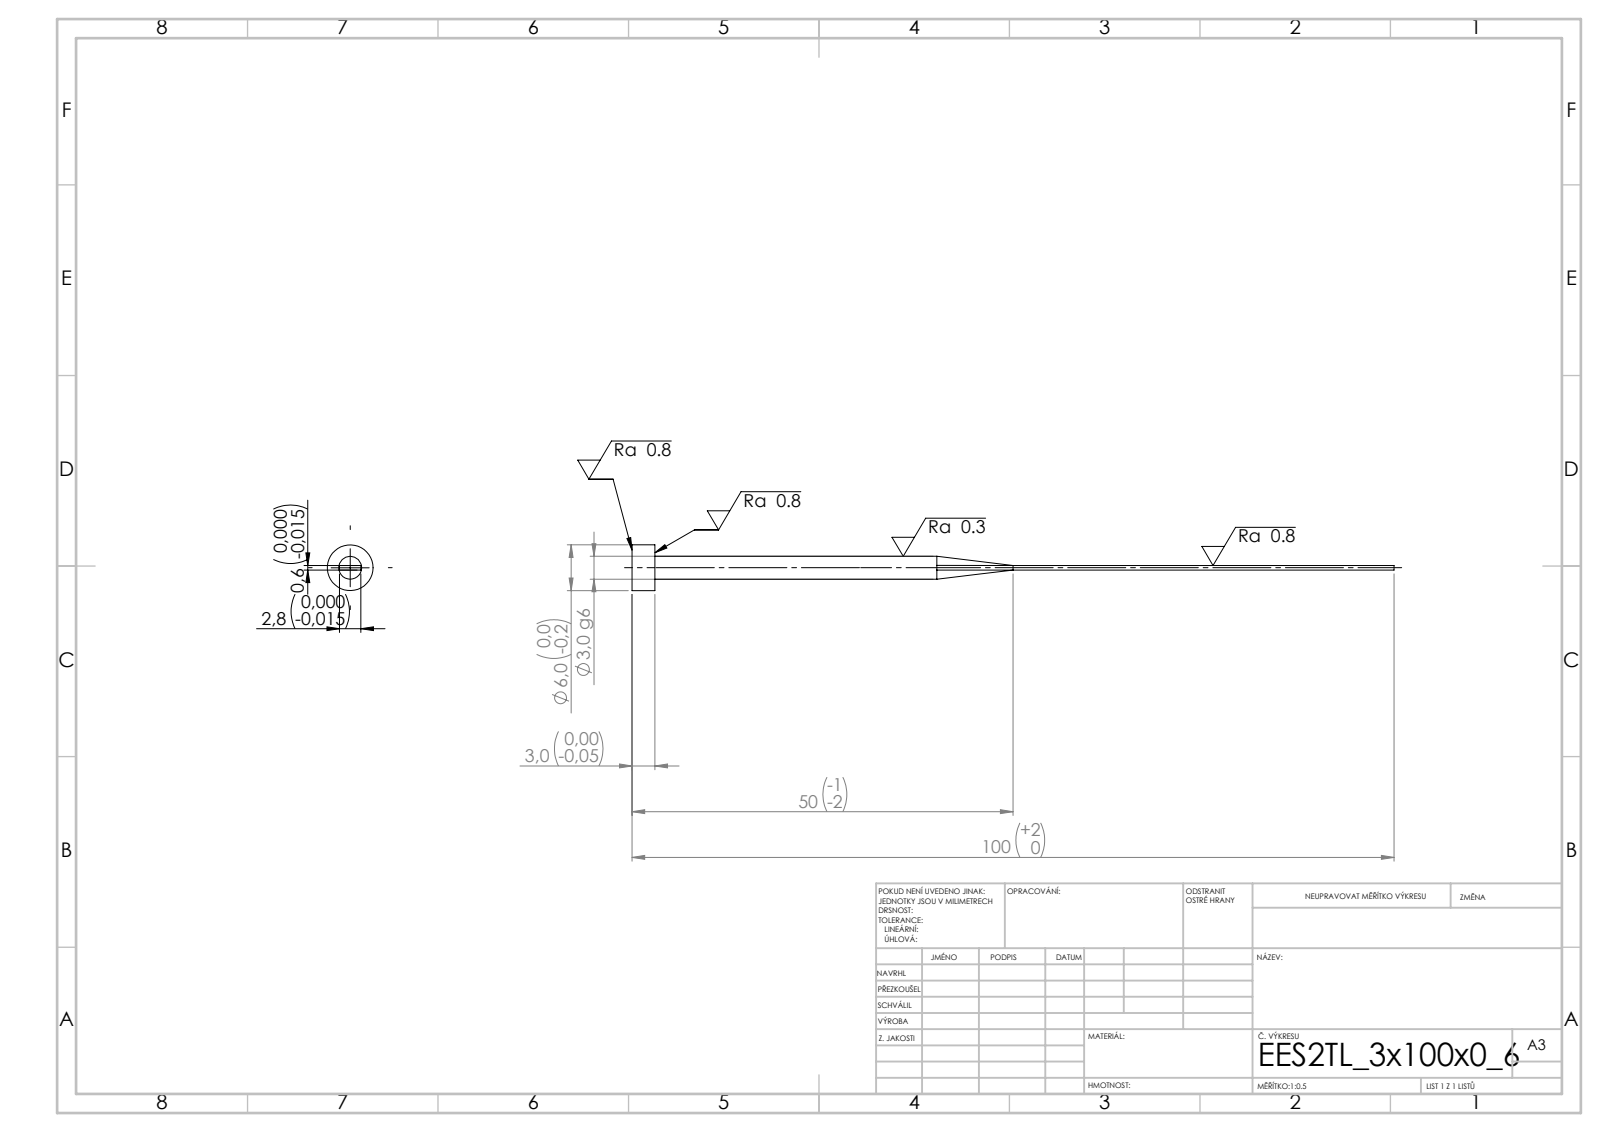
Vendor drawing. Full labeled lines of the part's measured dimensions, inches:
STEP written by: SolidWorks 2019 (CONFIG_CONTROL_DESIGN)
Units: inches
Bodies: 1 solid, 15 faces (7 planar, 4 cylindrical, 4 other)
Overall size (bounding box): 3.937 × 0.236 × 0.236
Volume: 0.029 in³ · Surface area: 1.35 in²
Round bosses / shafts (diameter × count): ⌀0.236 ×1, ⌀0.118 ×1
Main face-to-face distances: 0.024, 0.11, 0.118, 3.937, 3.819
